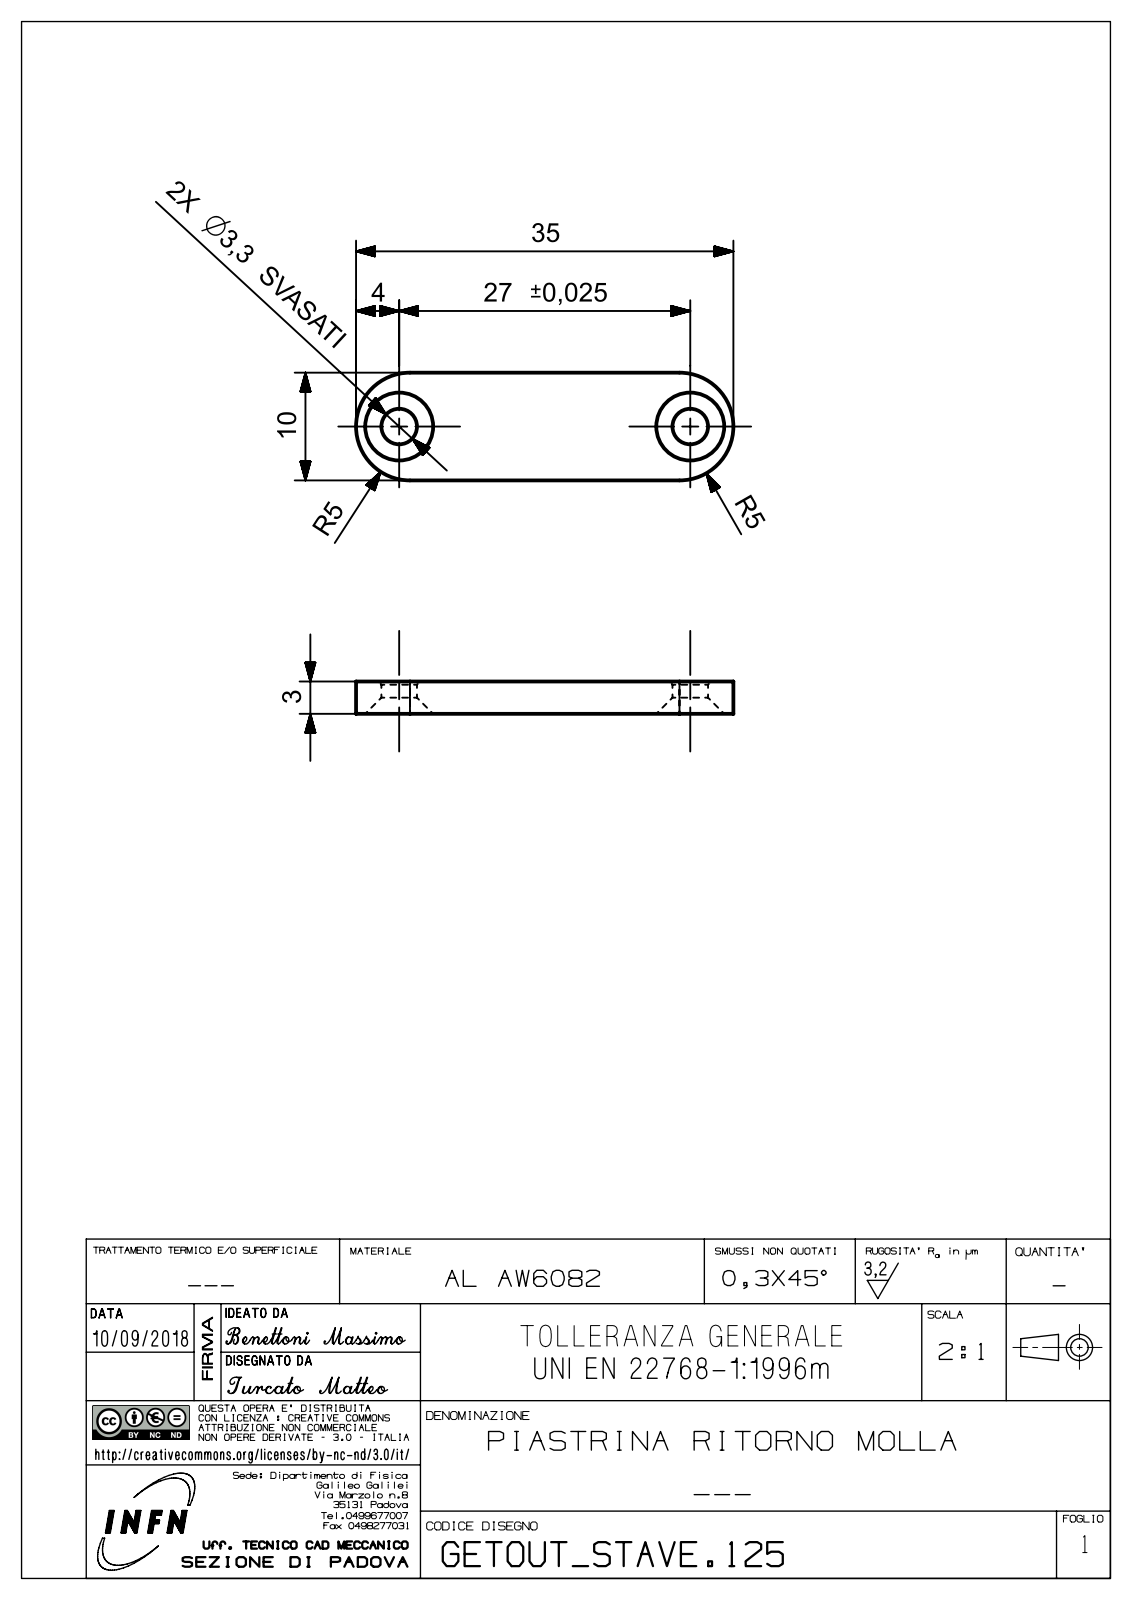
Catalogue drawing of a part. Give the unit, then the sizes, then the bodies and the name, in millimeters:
Units: millimetres
Overall size (bounding box): 35 × 10 × 3
Round holes (diameter × count): ⌀3.3 ×2
Partial cylindrical surfaces — rounded edges, fillets, slot ends (radius × count): R5 ×2
Main face-to-face distances: 3, 10
Hole centre spacings: 27
Volume: 903 mm³ · Surface area: 914 mm²
Bodies: 1 solid, 14 faces (4 planar, 6 cylindrical, 4 other)
Part name (STEP PRODUCT): bezA730AE56cd36
STEP written by: SIEMENS PLM Software NX 12.0 (AUTOMOTIVE_DESIGN)
